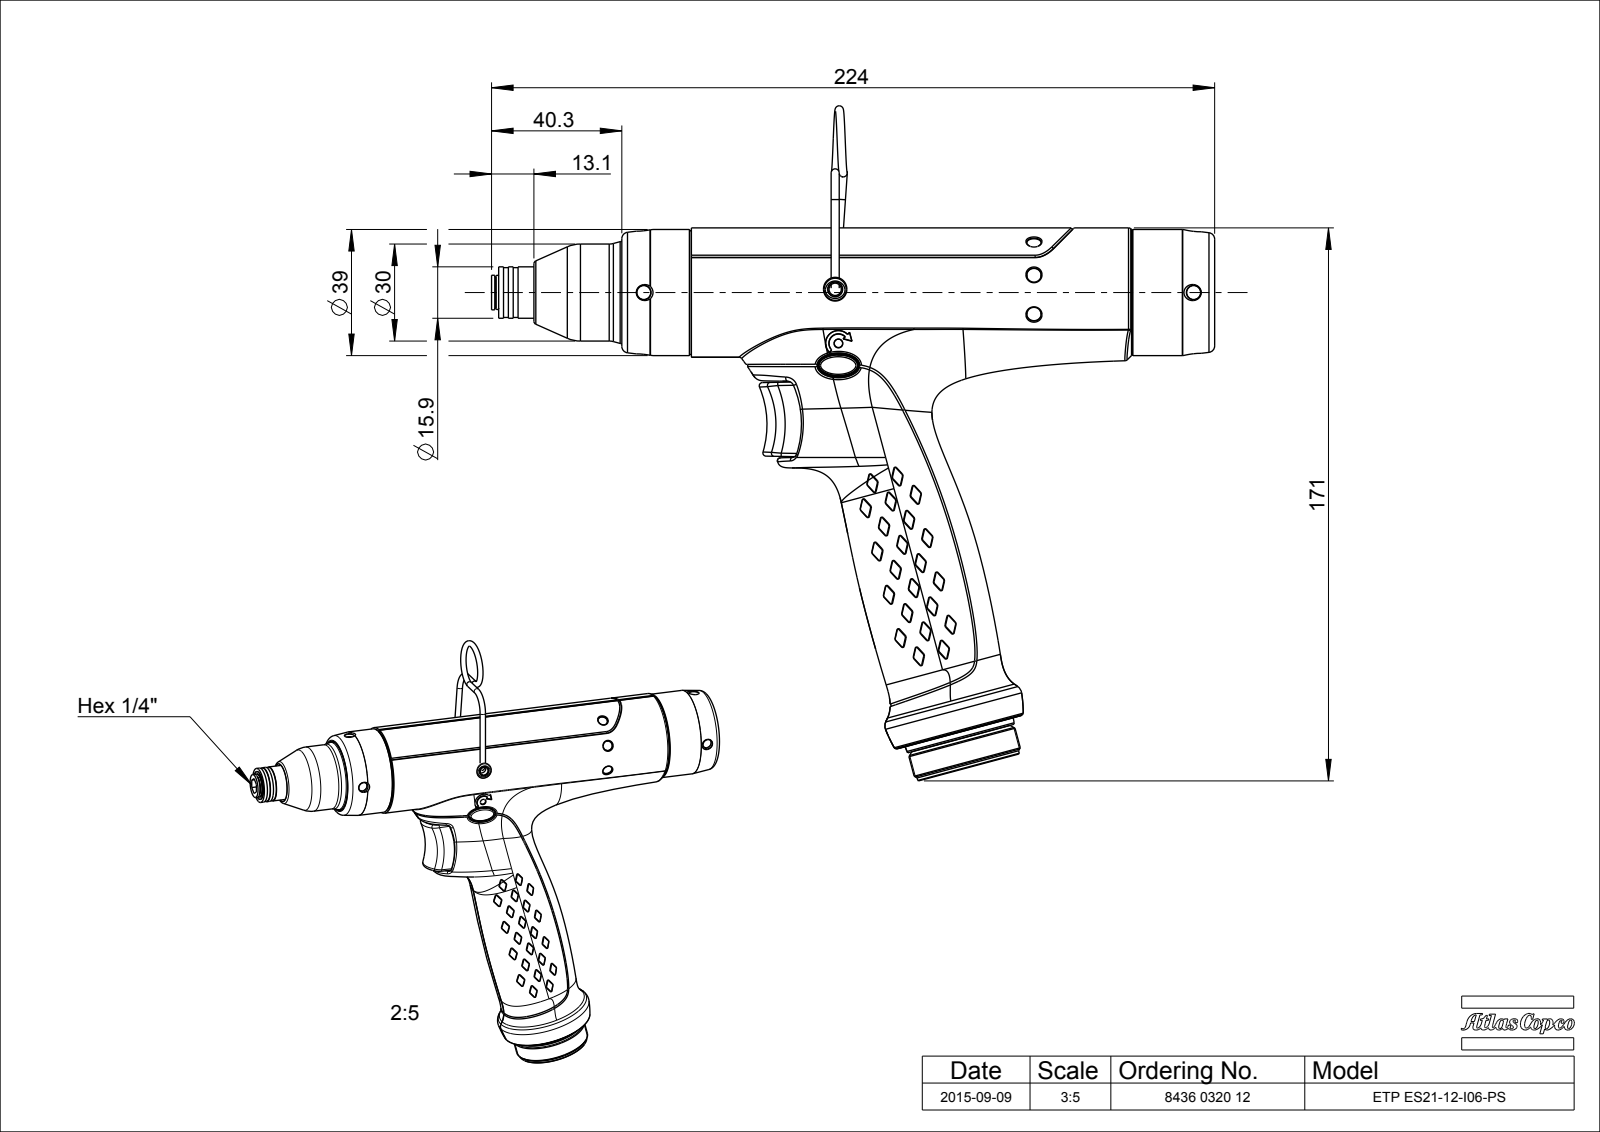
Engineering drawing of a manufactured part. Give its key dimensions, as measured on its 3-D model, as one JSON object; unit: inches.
{"part_name": "EXT_COMP_SW0008", "step_written_by": "CREO PARAMETRIC BY PTC INC, 2020281 (CONFIG_CONTROL_DESIGN)", "units": "inches", "bodies": {"solids": 2, "faces": 964, "planar": 101, "cylindrical": 122, "other": 741}, "overall_size": [8.807, 8.218, 1.717], "volume_in3": 23.66, "surface_area_in2": 77.64, "round_holes": [[0.177, 4], [0.071, 1], [0.15, 1], [1.154, 1]], "round_bosses_or_shafts": [[0.098, 4], [0.173, 2], [1.575, 1], [1.535, 1], [1.339, 1], [1.28, 1], [1.24, 1], [1.181, 1]], "partial_cylinders_radius": [[0.039, 9], [0.089, 6], [0.016, 4], [0.02, 4], [0.047, 4], [0.008, 2], [0.157, 1], [0.518, 1]], "face_to_face_distances": [4.972, 0.941, 1.848, 2.789, 1.004, 3.969, 8.721, 7.717, 3.748, 1.028], "hole_center_spacings": [6.697, 0.926, 2.331, 2.448, 4.366, 4.502]}
